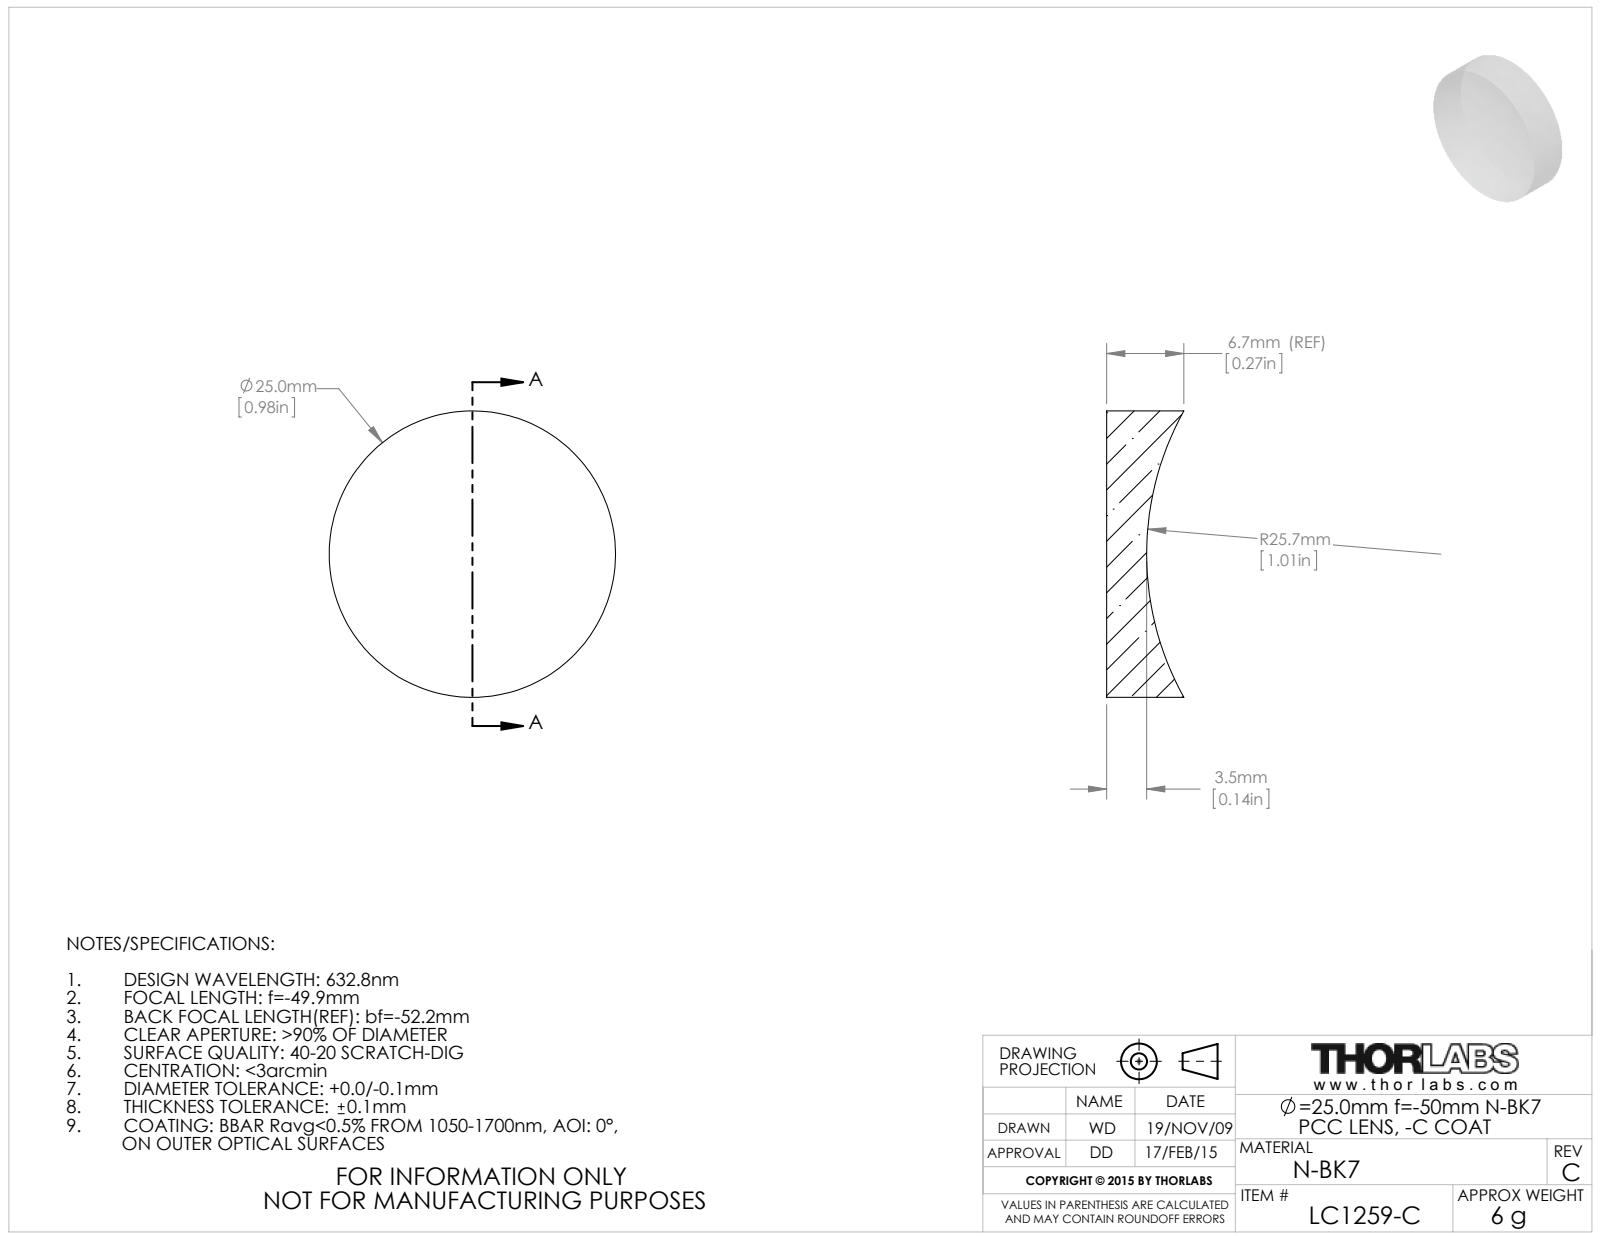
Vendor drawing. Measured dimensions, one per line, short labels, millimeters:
name: 19078-E0W
written by: SolidWorks 2009 (AUTOMOTIVE_DESIGN)
unit: mm
bodies: 1 solid, 5 faces (1 planar, 2 cylindrical, 2 other)
size: 25 × 25 × 6.75
volume: 2 497 mm³; area: 1 545 mm²
bosses: 1× ⌀25
